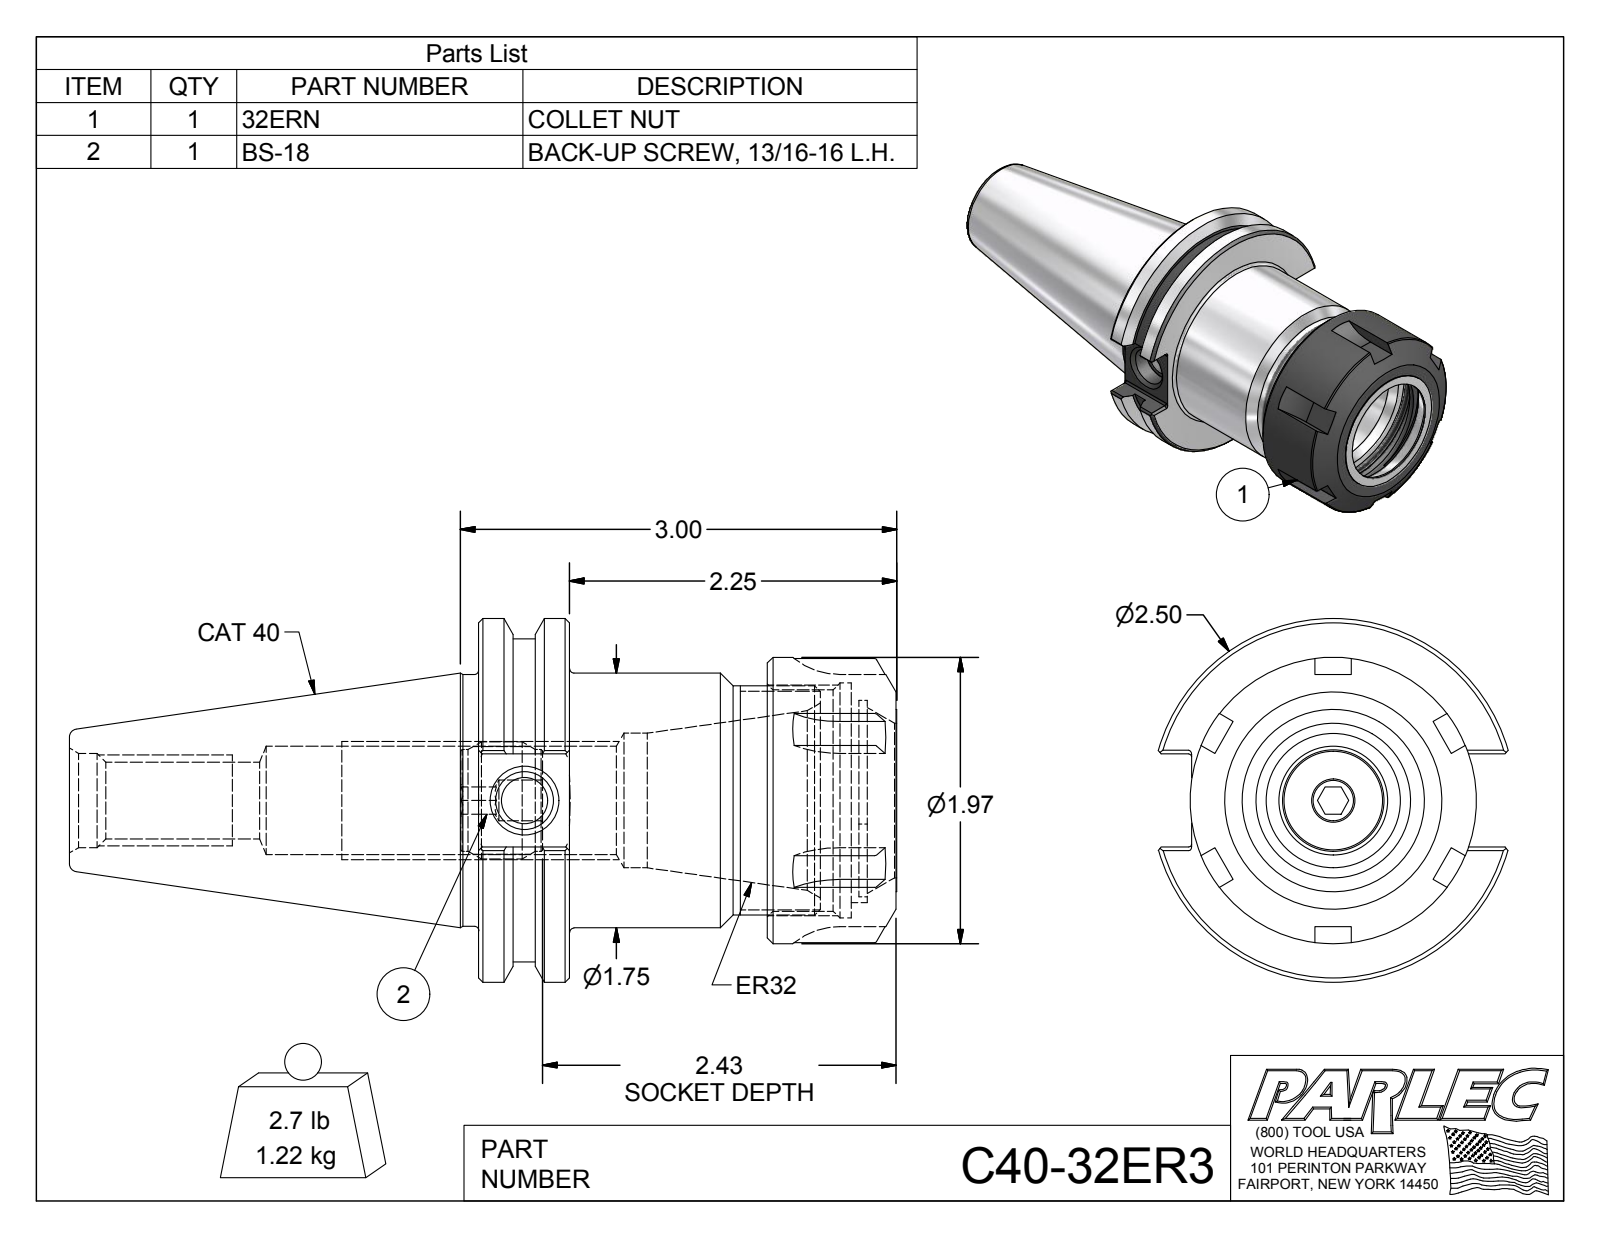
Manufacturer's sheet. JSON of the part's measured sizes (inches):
{"part_name": "C40-32ER3; C40-32ER3-1; 32ERN; BS-18", "step_written_by": "Autodesk Inventor 2012 (AUTOMOTIVE_DESIGN)", "units": "inches", "bodies": {"solids": 3, "faces": 148, "planar": 63, "cylindrical": 44, "other": 41}, "overall_size": [5.688, 2.5, 2.403], "volume_in3": 9.408, "surface_area_in2": 62.45, "round_holes": [[0.28, 1], [0.315, 1], [0.399, 1], [0.527, 1], [0.648, 1], [0.745, 1], [0.925, 1], [1.063, 1], [1.299, 1], [1.522, 1], [1.614, 1]], "round_bosses_or_shafts": [[2.5, 1], [2.219, 1], [1.969, 1], [1.75, 1], [1.73, 1], [1.575, 1], [1.252, 1], [0.805, 1]], "partial_cylinders_radius": [[0.02, 12], [0.5, 6], [0.689, 1]], "face_to_face_distances": [0.625, 1.984, 1.359, 2.563, 1.938, 0.579, 2.87, 2.245, 0.886, 0.307], "hole_center_spacings": [0.059]}
